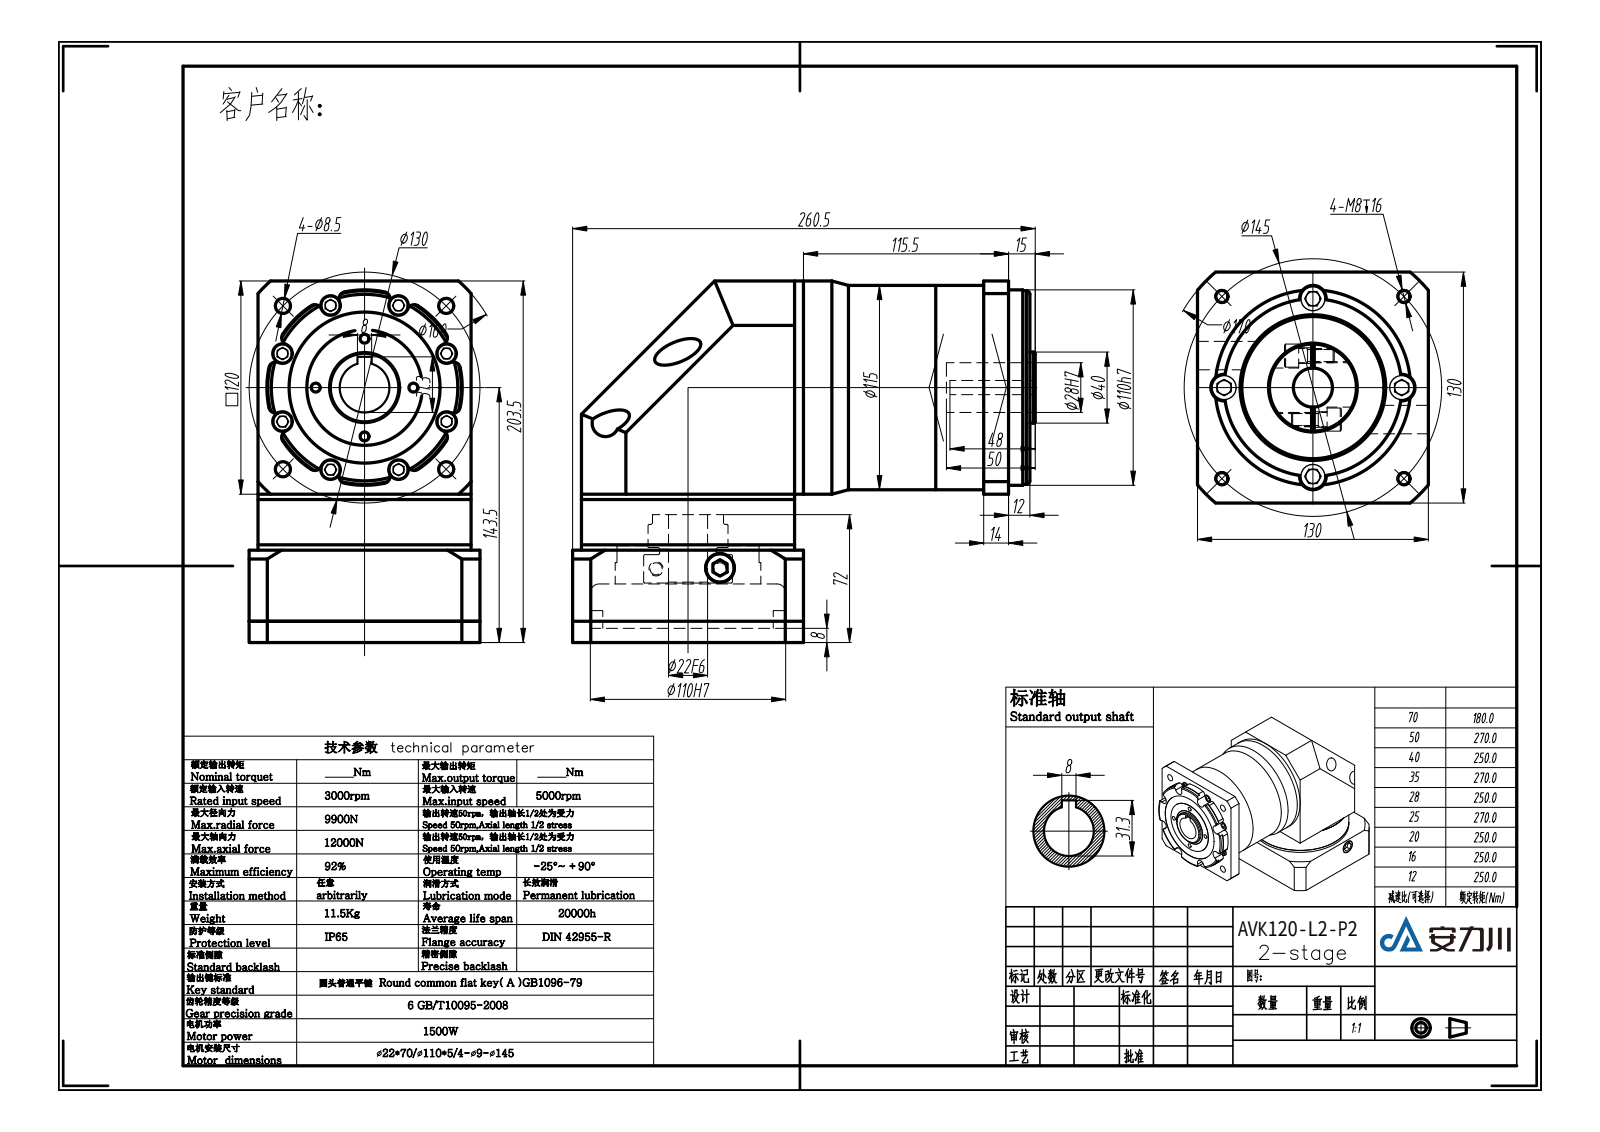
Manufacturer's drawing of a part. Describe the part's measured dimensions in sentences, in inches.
The part is named "VGZK115双级模型; VGZK115双级模型（22-70 110-5 4-9-145）; VGE115后过渡板（-70 110-5 4-9-145）". Its 3-D file was written by "SolidWorks 2016 (AUTOMOTIVE_DESIGN)". It is 23 solids with 523 faces: 277 planar, 217 cylindrical and 29 other. Overall it measures 10.256 by 8.012 by 5.118 inches. Its volume is 211.7 cubic inches and its surface area 602.7 square inches. Round holes: 8 of diameter 0.433, 6 of diameter 0.591, 4 of diameter 0.197, 4 of diameter 0.268, 4 of diameter 0.335, 4 of diameter 0.354, 2 of diameter 0.63, 1 of diameter 0.787, 1 of diameter 0.866, 1 of diameter 1.102, 1 of diameter 1.78, 1 of diameter 3.15. Round bosses or shafts: 10 of diameter 0.512, 8 of diameter 0.374, 2 of diameter 4.724, 2 of diameter 0.614, 1 of diameter 4.528, 1 of diameter 2.559, 1 of diameter 1.969, 1 of diameter 1.772. Partial cylindrical surfaces (rounded edges, fillets, slot ends): 16 of radius 0.157, 4 of radius 0.295, 1 of radius 2.146, 1 of radius 2.165, 1 of radius 3.15, 1 of radius 3.346. The main face-to-face distances are 0.197, 1.004, 1.936, 2.933, 3.13, 0.997, 1.194, 4.921, 4.724, 1.693. The hole center spacings are 2.854, 1.507, 2.784, 3.637, 3.728, 4.442, 0.098, 1.056.
